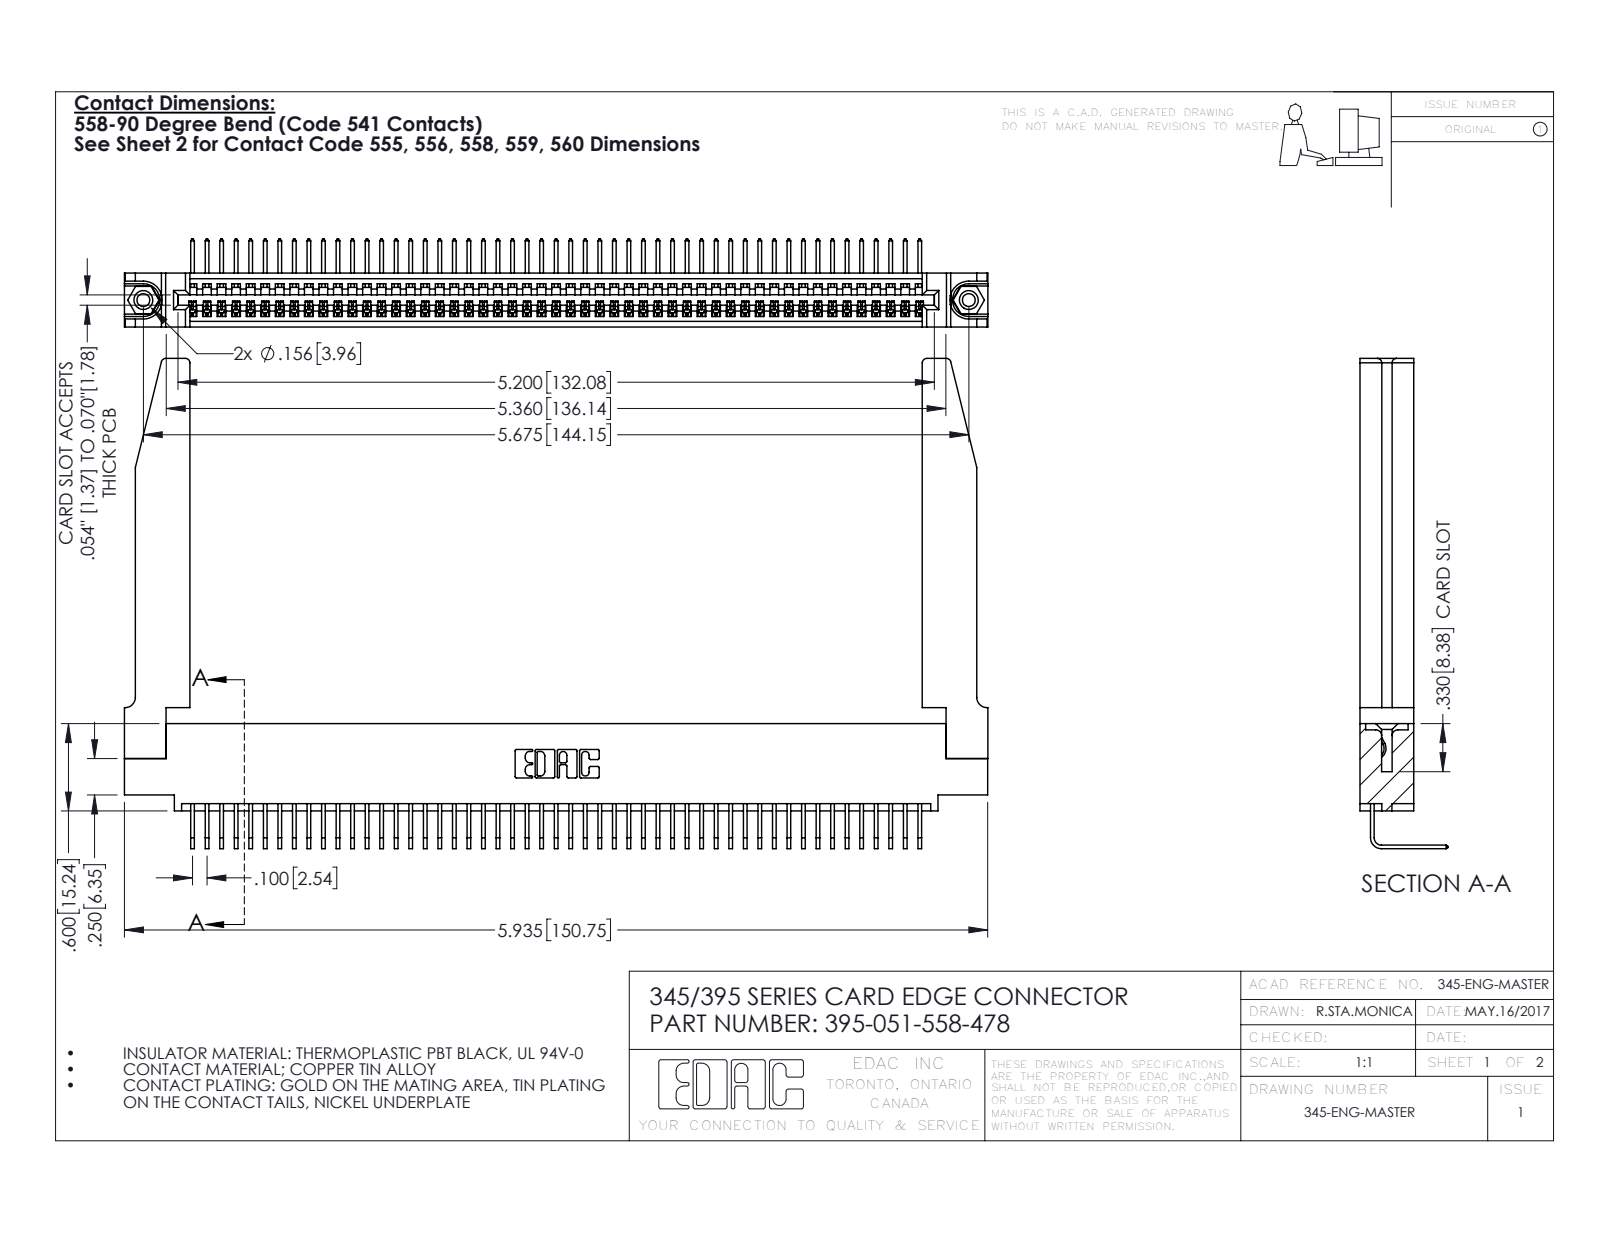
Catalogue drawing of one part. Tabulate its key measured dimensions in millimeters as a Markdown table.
| quantity | value |
| --- | --- |
| part name | 345-220-078_345-220-078; 345-292-001_558 Tail - 2; 395-051-558-478; 345-250-001_345-250-001-102 (+1 more) |
| STEP written by | SolidWorks 2016 (CONFIG_CONTROL_DESIGN) |
| units | millimeters |
| bodies | 56 solids, 3424 faces (2368 planar, 1004 cylindrical, 52 other) |
| overall size | 150.8 × 85.6 × 15.4 |
| volume | 22 250 mm³ |
| surface area | 27 300 mm² |
| round holes (diameter × count) | 2.3 × 2, 3.2 × 2, 4 × 2, 1.6 × 1 |
| round bosses / shafts (diameter × count) | 3.9 × 2 |
| partial cylindrical surfaces (radius × count) | 0.2 × 102, 0.3 × 22, 0.8 × 8, 0.2 × 6, 0.8 × 6, 0.7 × 3, 0.8 × 2, 1 × 2 |
| main face-to-face distances | 9.4, 1.8, 7.6, 5.1, 2.5, 6.9, 0.6, 5.7, 3.8, 3.8 |
| hole center spacings | 6.9, 138.2, 144.1 |
